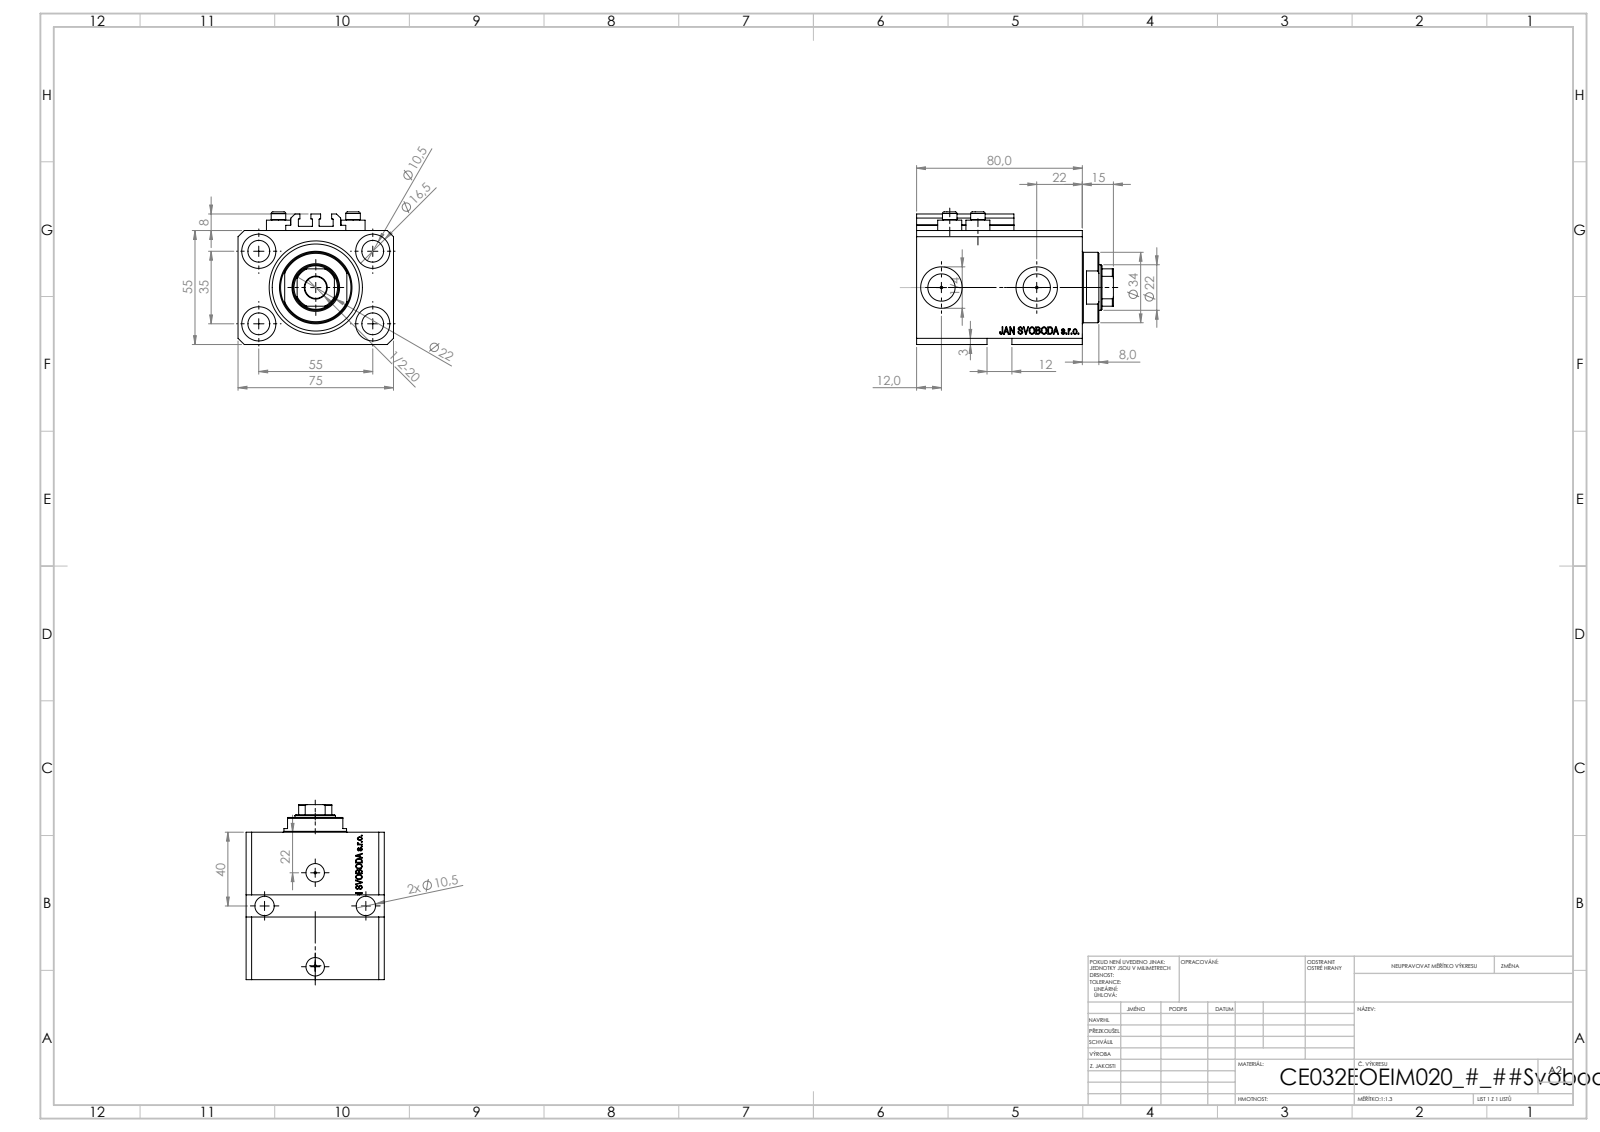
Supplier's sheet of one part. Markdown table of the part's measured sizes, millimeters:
| quantity | value |
| --- | --- |
| part name | V250CE_VC_E; V250CE_E_Body; ALLEN BOLT V250CE; V250CE_C_VCP |
| STEP written by | SolidWorks 2019 (CONFIG_CONTROL_DESIGN) |
| units | millimeters |
| bodies | 8 solids, 1064 faces (514 planar, 126 cylindrical, 424 other) |
| overall size | 95 × 75 × 64 |
| volume | 283 894 mm³ |
| surface area | 74 463 mm² |
| round holes (diameter × count) | 10.5 × 7, 1.25 × 4, 4 × 4, 16.5 × 4, 10 × 2, 13.16 × 2, 20 × 2, 22 × 1, 32 × 1, 45 × 1 |
| round bosses / shafts (diameter × count) | 11.6 × 4, 7 × 4, 34 × 1 |
| partial cylindrical surfaces (radius × count) | 0.2 × 10, 10.5 × 1 |
| main face-to-face distances | 55, 75, 15, 80, 65, 3, 55.1, 9.9, 70.1, 54 |
| hole center spacings | 32.6, 55, 13.6, 14.09, 19.89, 20.12, 25.81, 28.48 |
